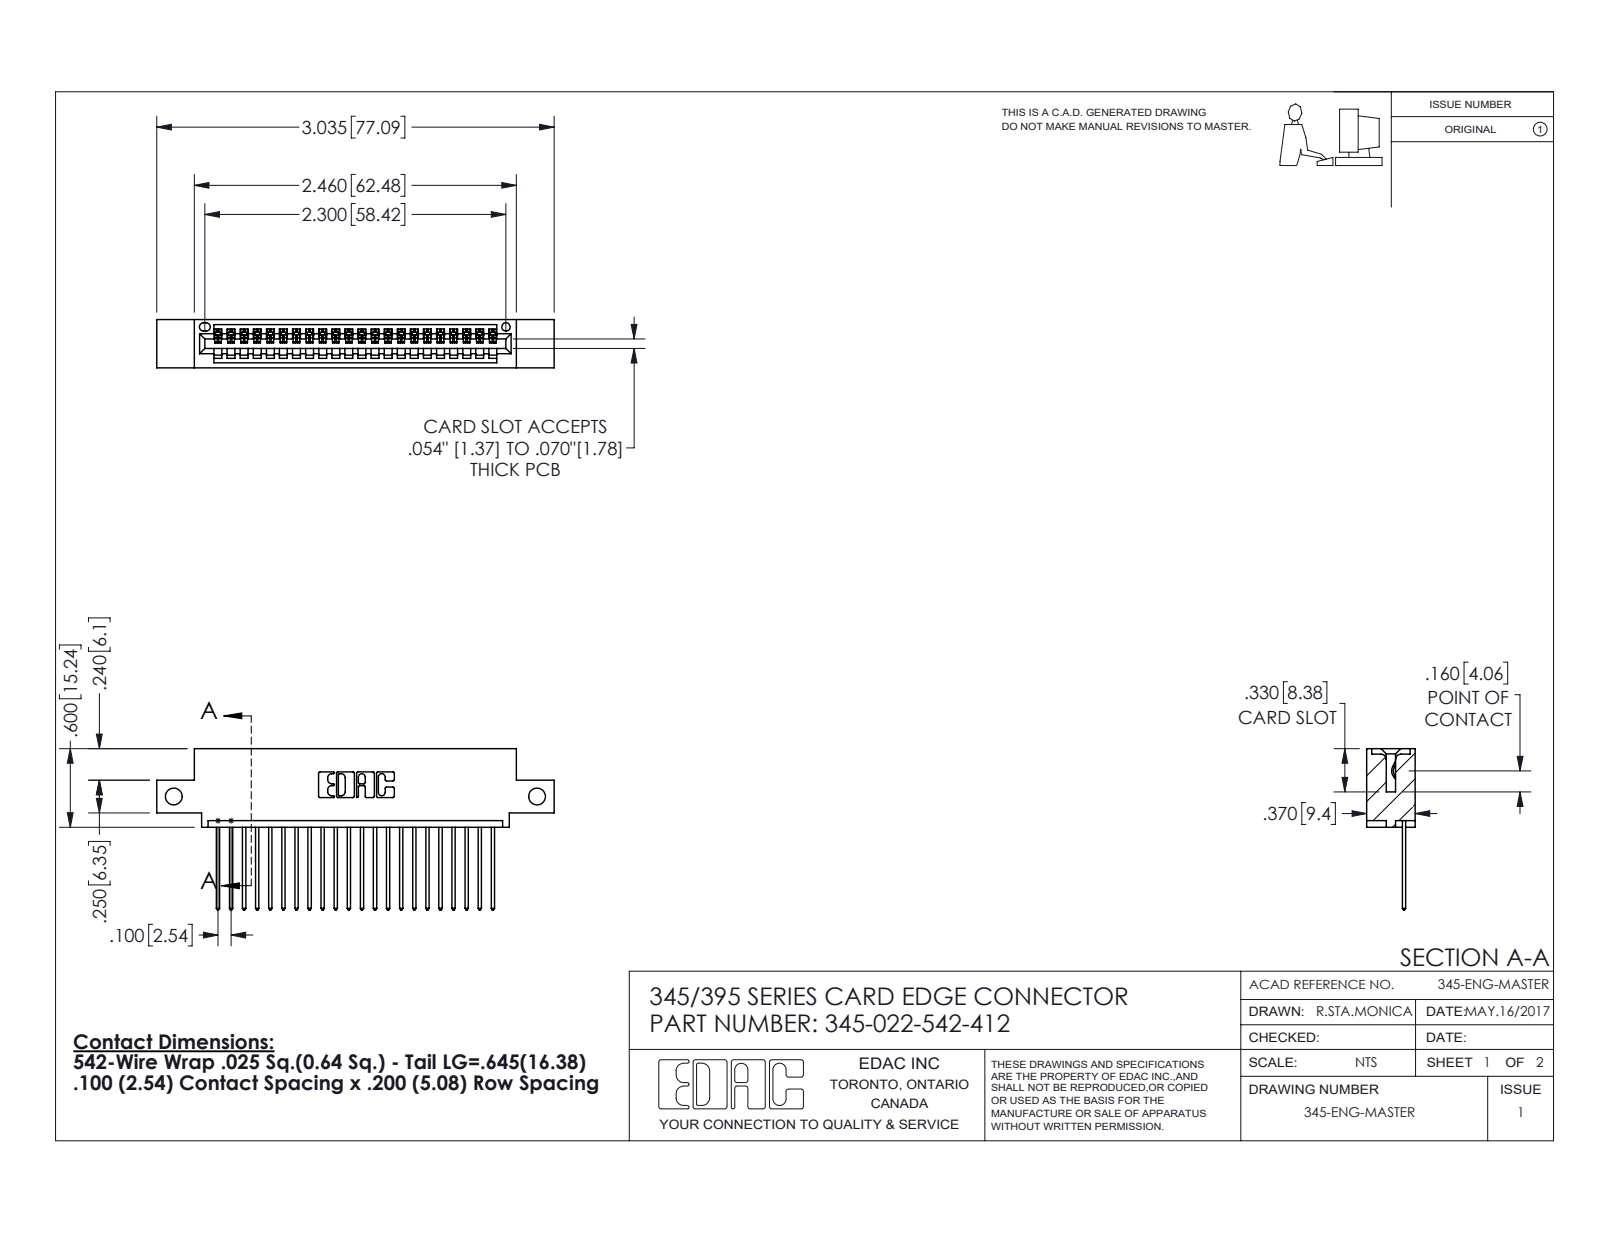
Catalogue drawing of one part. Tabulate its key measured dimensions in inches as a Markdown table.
| quantity | value |
| --- | --- |
| part name | 345 Part_0.110 Offset - Side Mount; 345-292-001_345-293-142; 345-022-542-412 |
| STEP written by | SolidWorks 2016 (CONFIG_CONTROL_DESIGN) |
| units | inches |
| bodies | 23 solids, 1406 faces (964 planar, 442 cylindrical, 0 other) |
| overall size | 3.035 × 1.232 × 0.37 |
| volume | 0.43 in³ |
| surface area | 14.48 in² |
| round holes (diameter × count) | 0.128 × 2, 0.064 × 1 |
| partial cylindrical surfaces (radius × count) | 0.006 × 44, 0.01 × 44, 0.01 × 22, 0.007 × 6, 0.031 × 6, 0.026 × 3, 0.031 × 2, 0.04 × 2 |
| main face-to-face distances | 0.298, 0.072, 0.37, 0.2, 0.098, 0.272, 0.025, 0.225, 0.149, 0.072 |
| hole center spacings | 2.775 |
